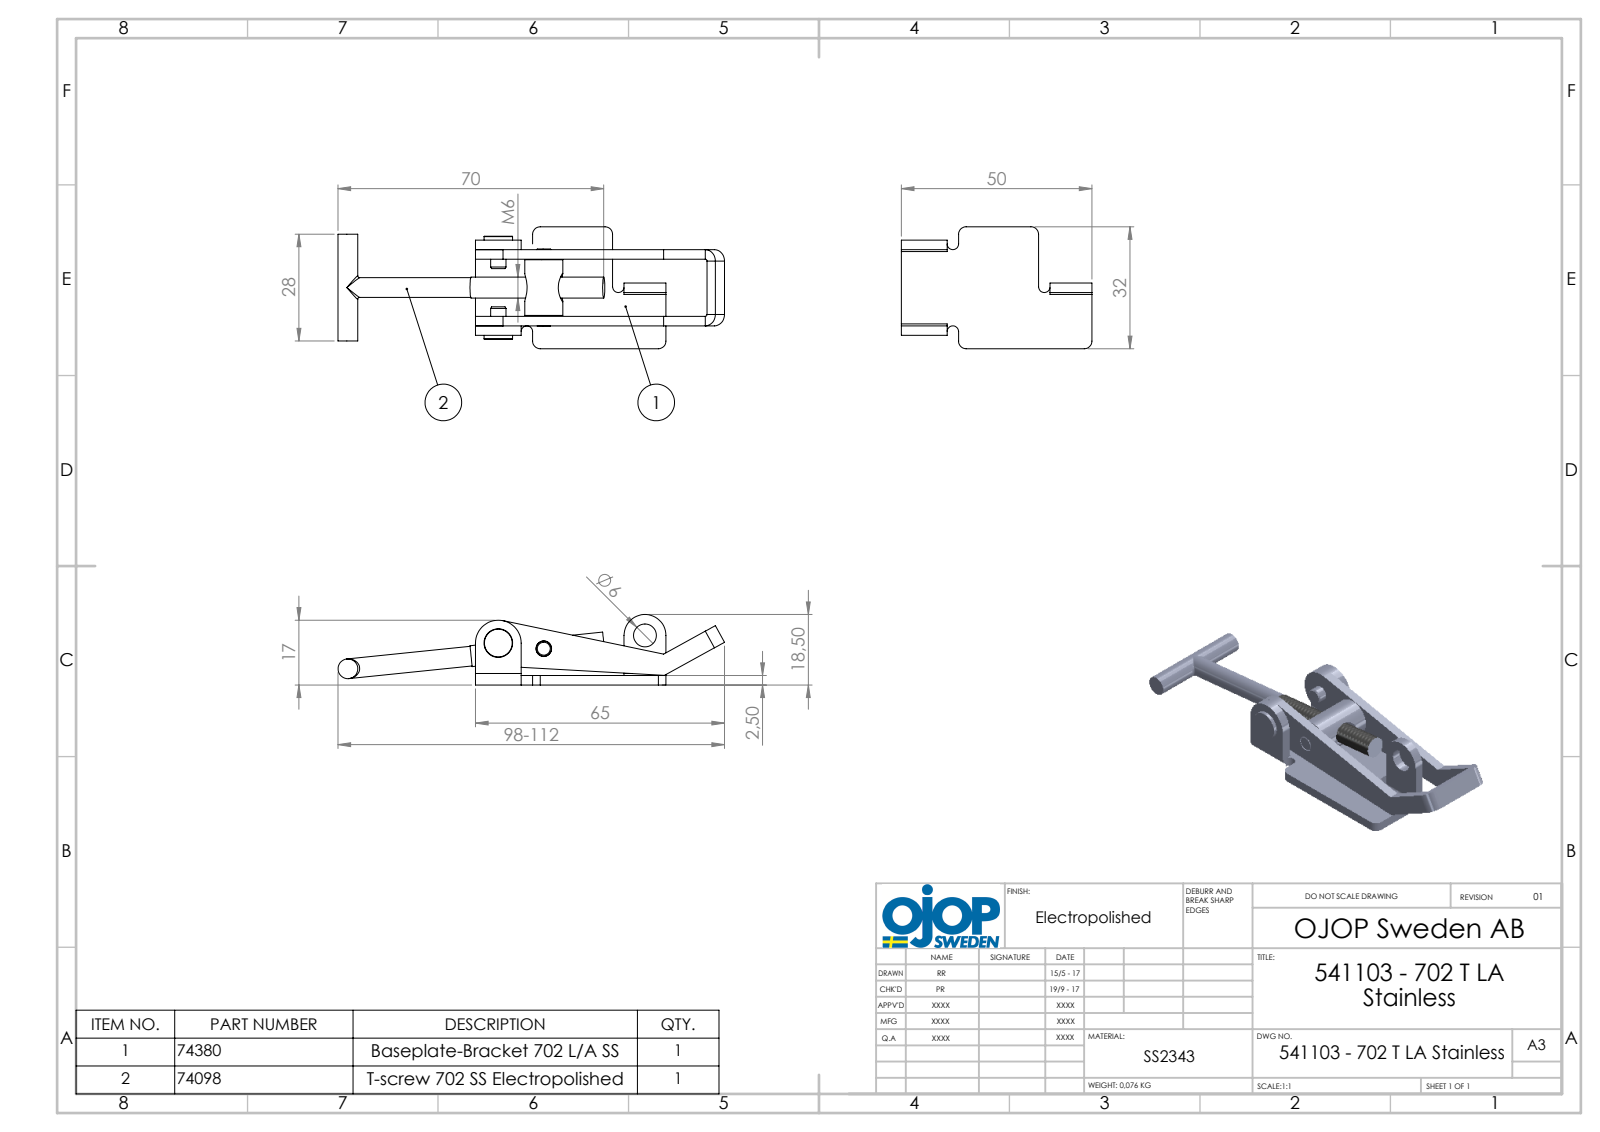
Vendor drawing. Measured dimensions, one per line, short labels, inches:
name: 541103 - 702 T LA Stainless; 702 - T-skruv M6; 702 - Ansatsnit; 702 - Rulle (+2 more)
written by: SolidWorks 2015 (AUTOMOTIVE_DESIGN)
unit: in
bodies: 6 solids, 149 faces (66 planar, 65 cylindrical, 18 other)
size: 4.047 × 1.26 × 0.728
volume: 0.631 in³; area: 15.38 in²
holes: 2× ⌀0.161, 2× ⌀0.236, 1× ⌀0.197
bosses: 2× ⌀0.208, 2× ⌀0.157, 1× ⌀0.394, 1× ⌀0.295, 1× ⌀0.236
rounds: 5× R0.02, 5× R0.118, 4× R0.079, 2× R0.059, 1× R0.059, 1× R0.217, 1× R0.236
face distances: 0.098, 0.689, 0.787, 0.344, 0.443, 0.591, 0.197, 0.246, 0.886, 0.236
hole spacings: 0.473, 1.055, 1.518
